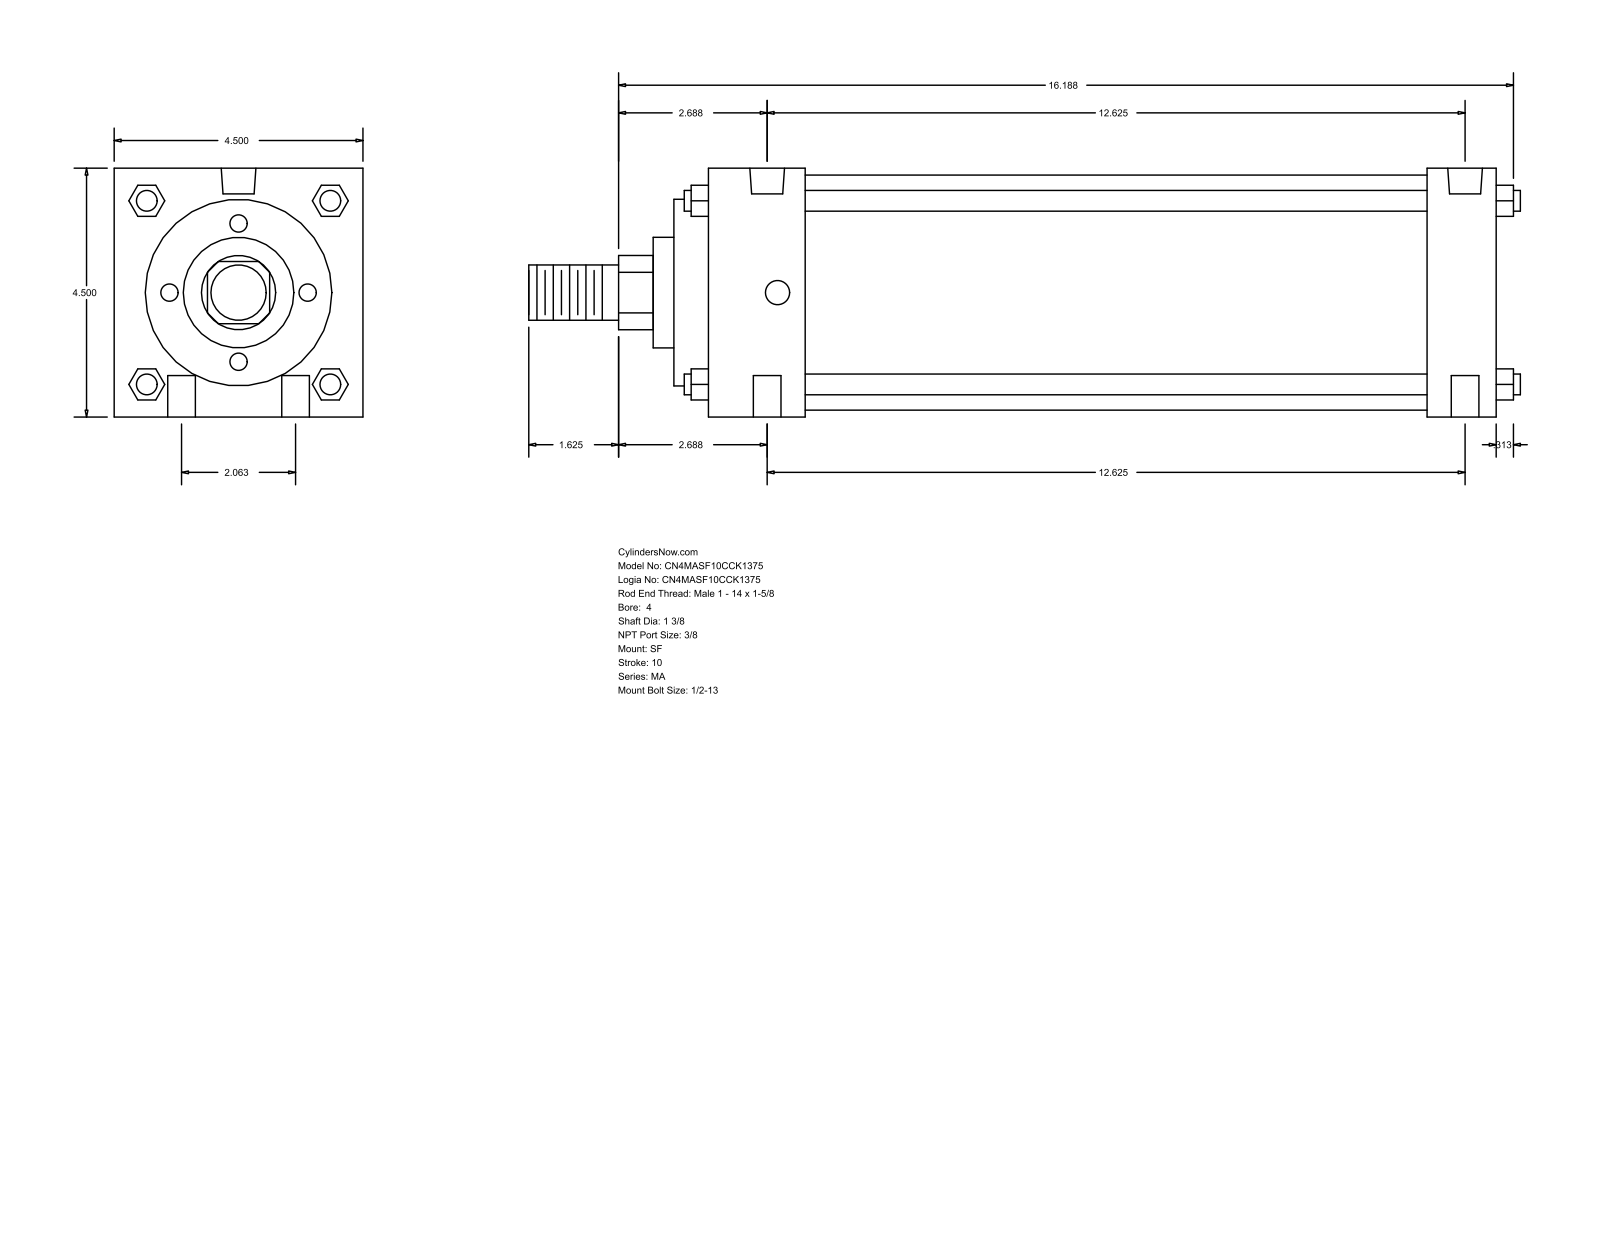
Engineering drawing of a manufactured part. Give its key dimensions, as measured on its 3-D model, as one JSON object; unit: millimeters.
{"part_name": "MA_SF__0400_1.375", "step_written_by": "GSSL Pune (CONFIG_CONTROL_DESIGN)", "units": "millimeters", "bodies": {"solids": 0, "faces": 126, "planar": 95, "cylindrical": 31, "other": 0}, "overall_size": [455.61, 114.3, 114.3], "round_holes": [[12.7, 4], [11.11, 2], [15.93, 2]], "round_bosses_or_shafts": [[9.53, 4], [107.95, 1], [85.72, 1], [50.8, 1], [34.92, 1], [25.4, 1]], "partial_cylinders_radius": [[17.06, 1]], "face_to_face_distances": [114.3, 361.96, 15.87, 377.83, 346.08, 330.21, 31.75, 60.32, 44.45, 285.76], "hole_center_spacings": [26.19, 321.75, 320.68, 52.38, 324.93, 311.15]}
